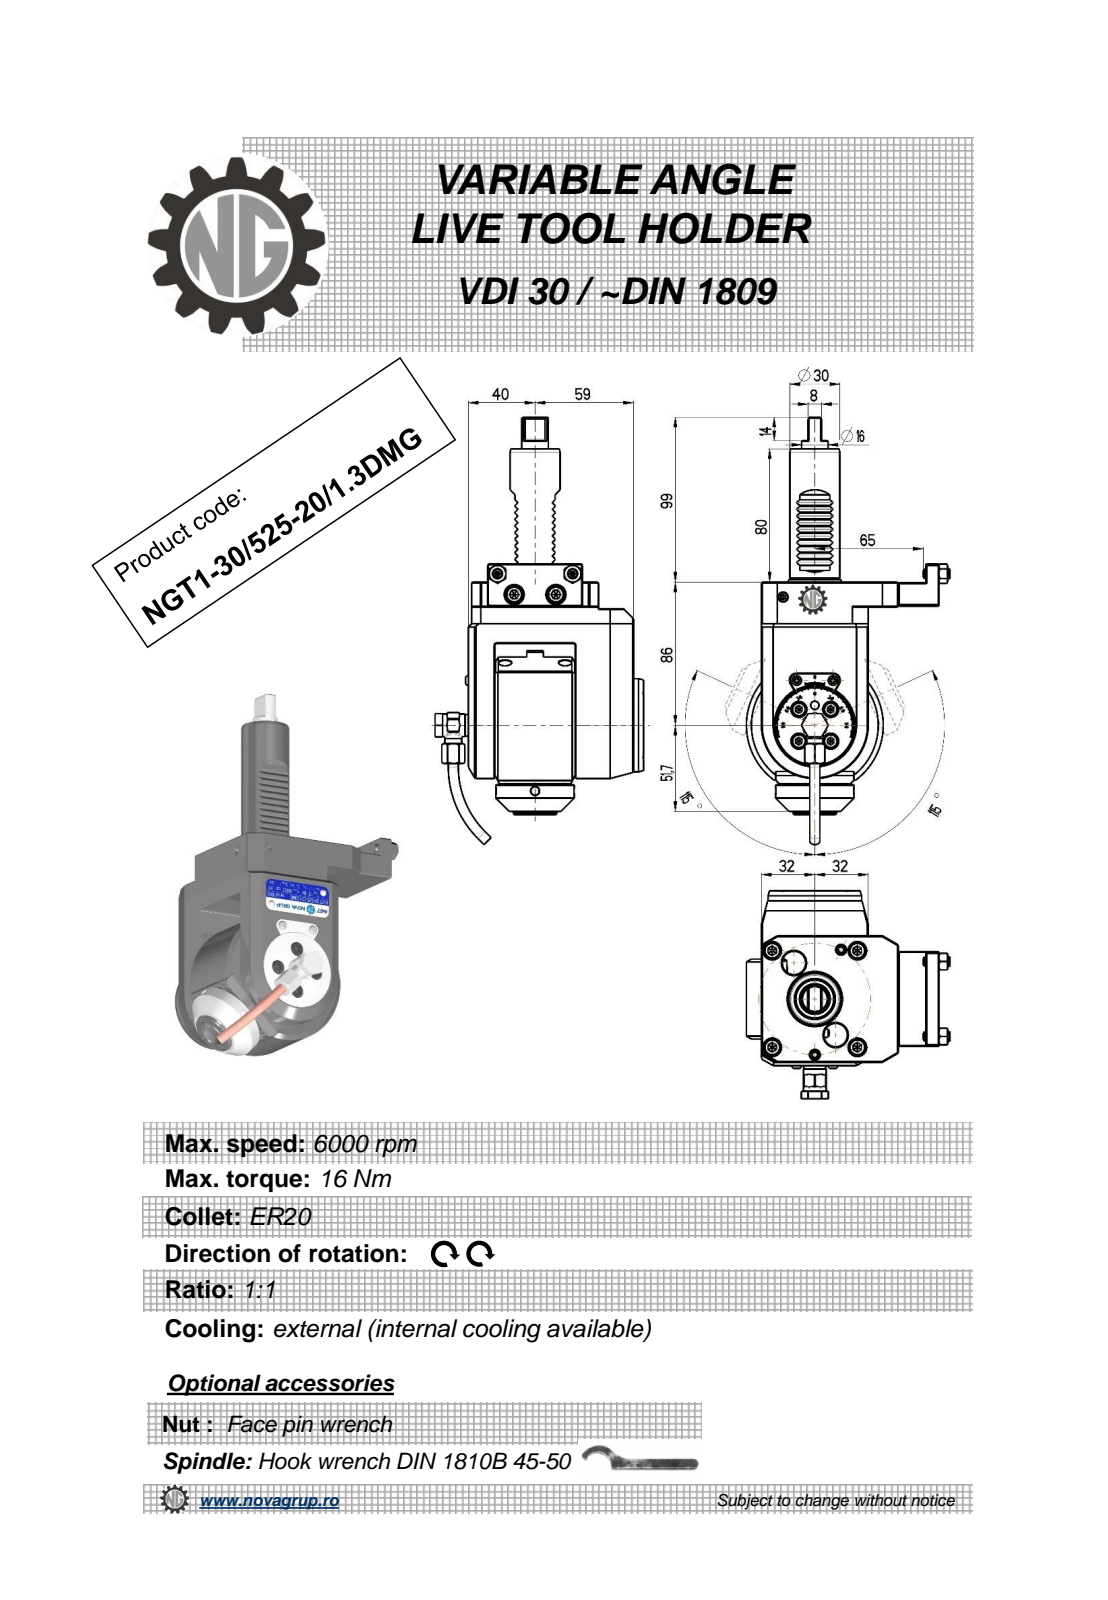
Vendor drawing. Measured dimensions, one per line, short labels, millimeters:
name: NGT1_30_525_20_1_3DMG
written by: PRO/ENGINEER BY PARAMETRIC TECHNOLOGY CORPORATION, 2010280 (CONFIG_CONTROL_DESIGN)
unit: mm
bodies: 1 solid, 547 faces (246 planar, 139 cylindrical, 162 other)
size: 256.67 × 124.9 × 122
volume: 829 334 mm³; area: 81 504 mm²
holes: 4× ⌀3.2, 3× ⌀4, 2× ⌀3, 2× ⌀5, 1× ⌀6.2, 1× ⌀9, 1× ⌀10, 1× ⌀11, 1× ⌀16
bosses: 4× ⌀6, 2× ⌀10, 2× ⌀5.7, 1× ⌀82, 1× ⌀56, 1× ⌀47, 1× ⌀36, 1× ⌀30
rounds: 20× R0.3, 10× R0.31, 4× R0.5, 2× R0.8, 2× R1, 1× R7.7, 1× R32
face distances: 64, 14, 0.5, 16, 37, 99, 48, 14.5, 62, 6
hole spacings: 10.75, 15.2, 21.5, 50.17, 50.56, 0.4, 38.25, 38.65
